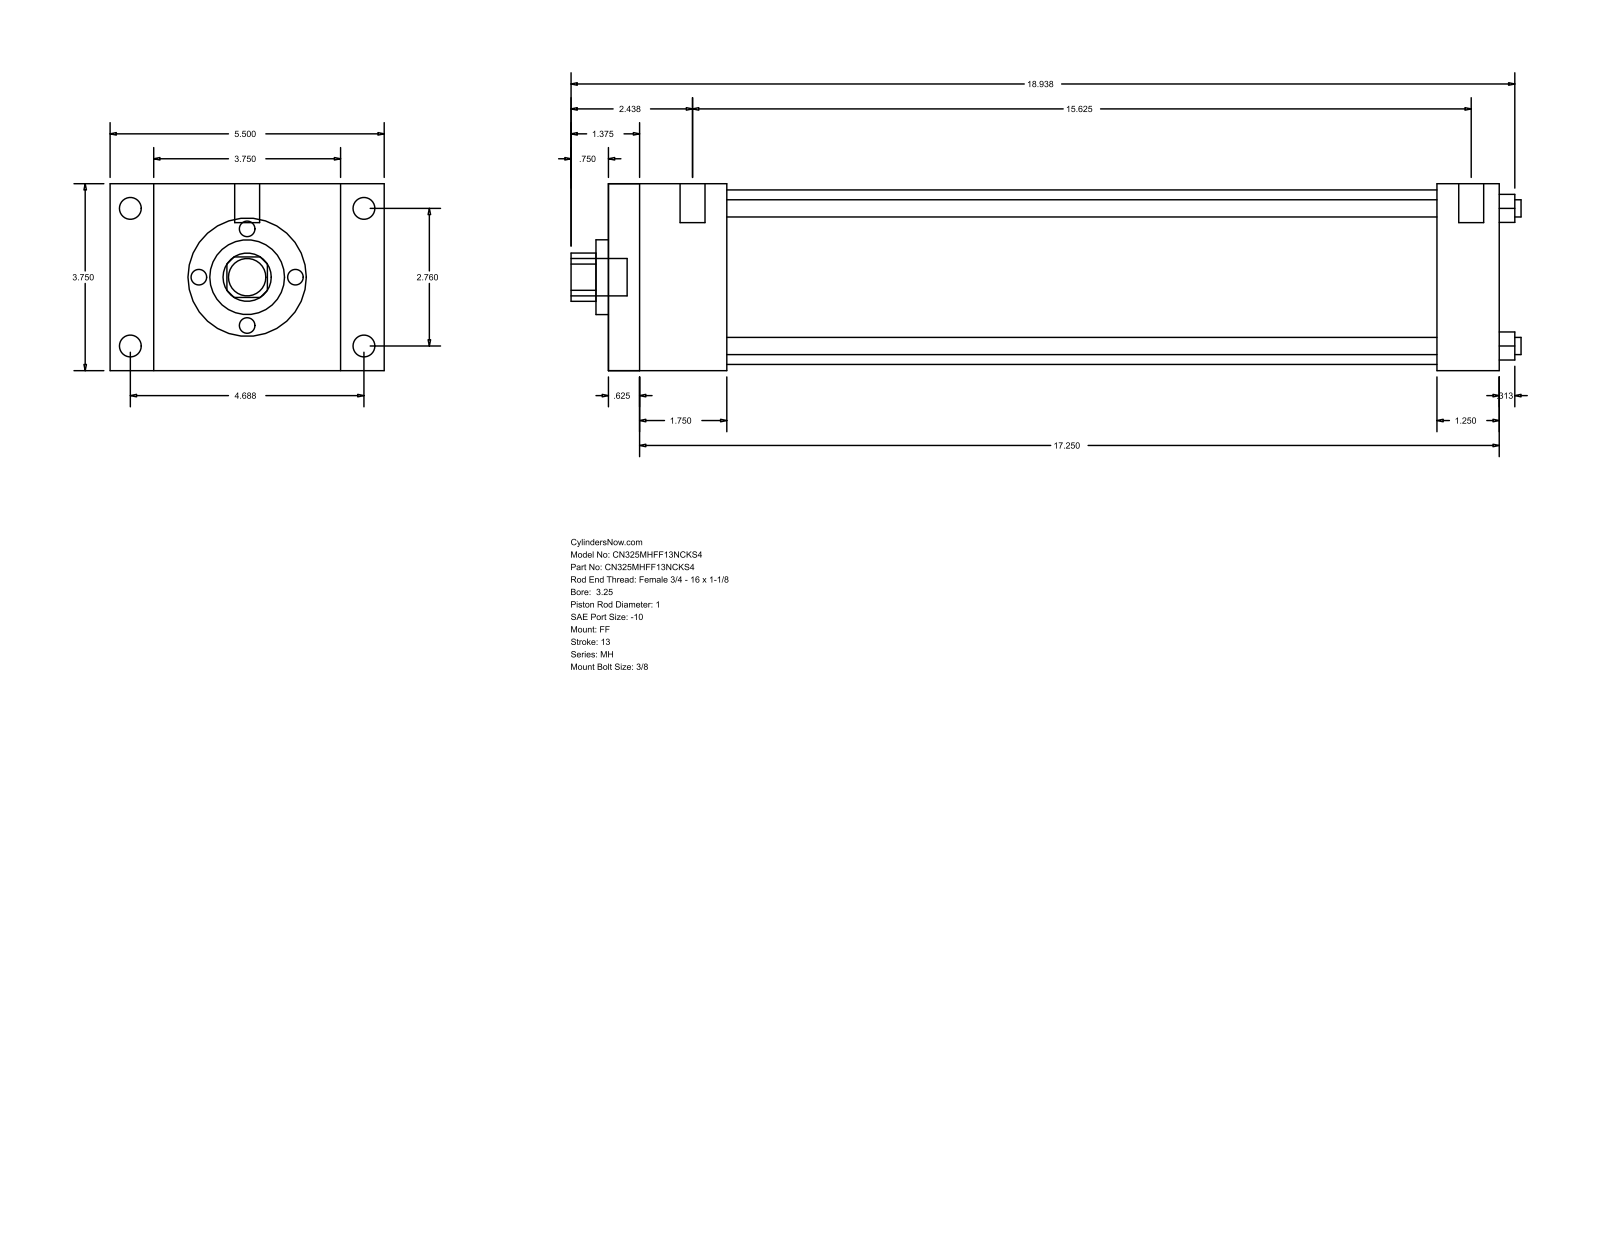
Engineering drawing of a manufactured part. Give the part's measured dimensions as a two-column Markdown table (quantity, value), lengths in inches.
| quantity | value |
| --- | --- |
| part name | MH_FF__0325_1 |
| STEP written by | GSSL Pune (CONFIG_CONTROL_DESIGN) |
| units | inches |
| bodies | 0 solids, 92 faces (64 planar, 28 cylindrical, 0 other) |
| overall size | 19.063 × 5.5 × 3.75 |
| round holes (diameter × count) | 0.345 × 4, 1 × 1, 1.5 × 1, 3.5 × 1 |
| round bosses / shafts (diameter × count) | 0.438 × 4, 0.219 × 4, 0.5 × 2, 0.75 × 1 |
| partial cylindrical surfaces (radius × count) | 0.484 × 1 |
| main face-to-face distances | 3.75, 17.875, 0.625, 17.25, 0.875, 4.625, 16.625, 16, 1.25, 2.375 |
| hole center spacings | 1.952, 2.76, 3.903 |
